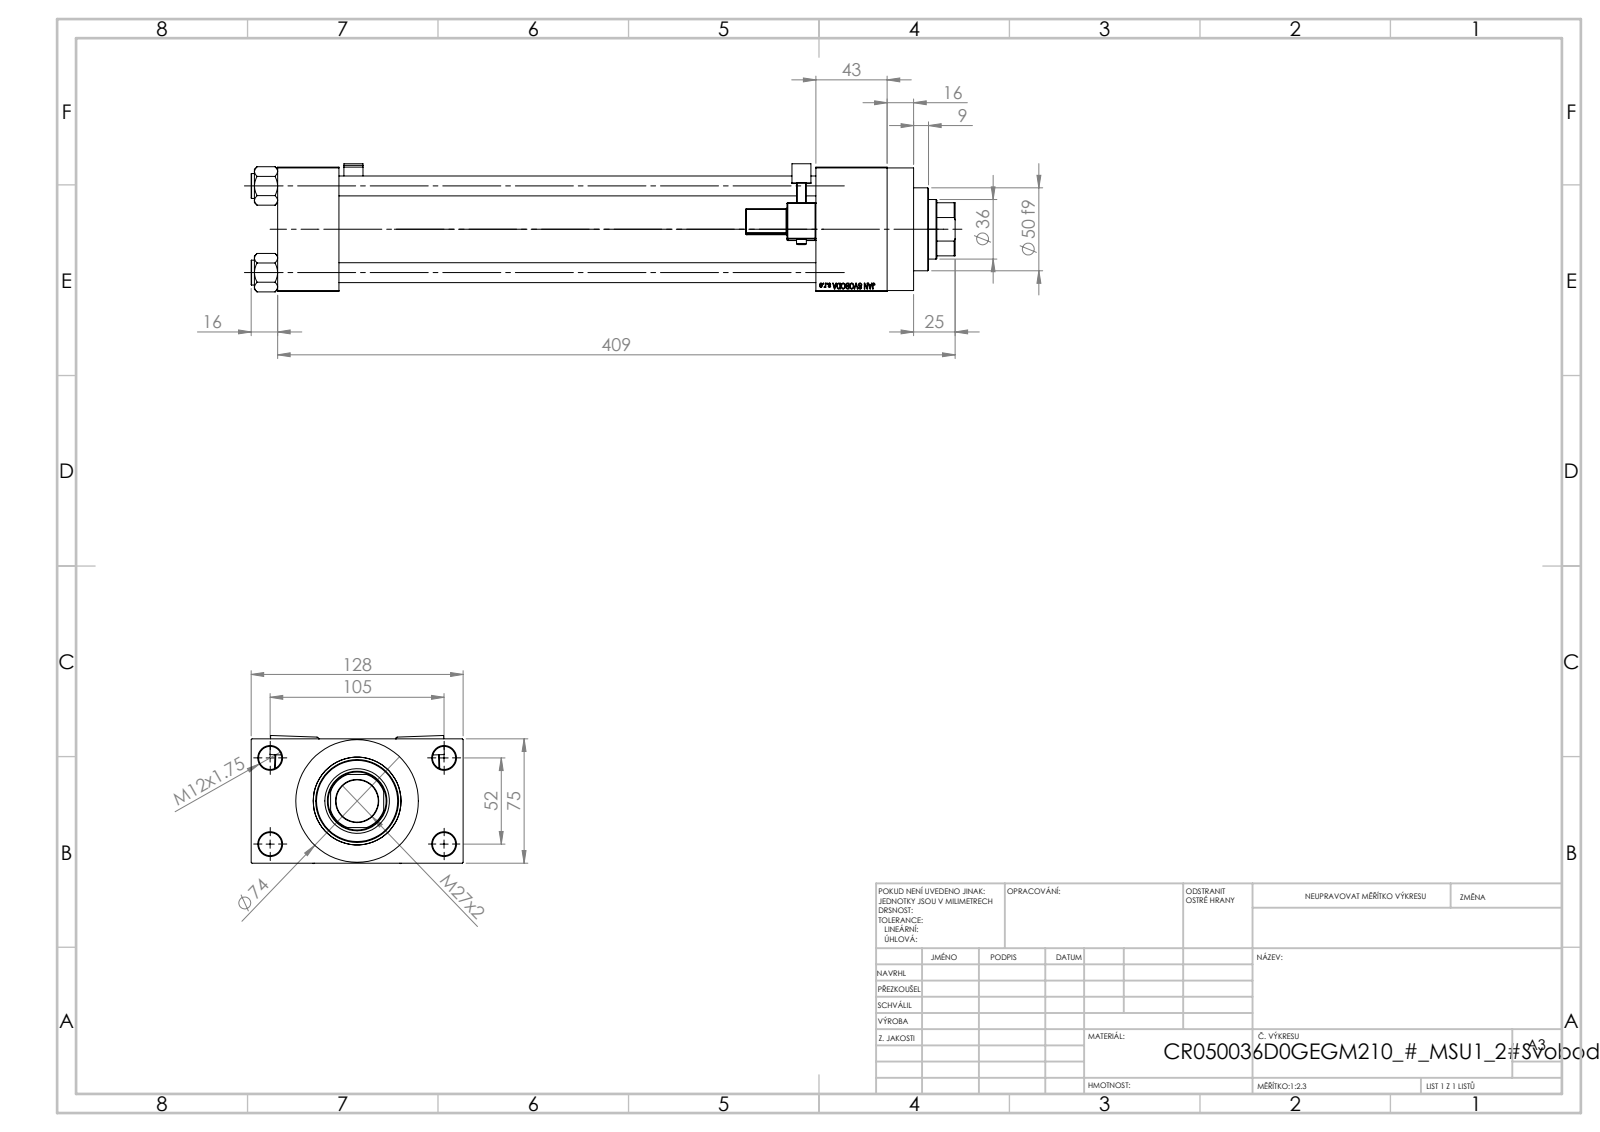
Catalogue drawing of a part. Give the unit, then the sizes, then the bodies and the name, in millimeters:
Units: millimetres
Overall size (bounding box): 425 × 128 × 77.3
Round holes (diameter × count): ⌀12 ×4, ⌀14 ×4, ⌀7 ×2, ⌀20.96 ×2, ⌀30 ×2, ⌀25.5 ×1, ⌀36 ×1, ⌀39 ×1, ⌀41 ×1, ⌀53 ×1
Round bosses / shafts (diameter × count): ⌀15 ×4, ⌀6 ×2, ⌀74 ×1, ⌀56 ×1, ⌀50 ×1
Partial cylindrical surfaces — rounded edges, fillets, slot ends (radius × count): R0.5 ×48, R1 ×2, R2.5 ×2, R4 ×2, R17.5 ×1
Main face-to-face distances: 75, 288, 101.5, 37, 325, 26.5, 43, 368, 331, 16
Hole centre spacings: 26.35, 36.98, 52.3, 58.43, 58.59, 78.65, 94.37, 52
Volume: 1 321 000 mm³ · Surface area: 323 344 mm²
Bodies: 13 solids, 1258 faces (555 planar, 149 cylindrical, 554 other)
Part name (STEP PRODUCT): V215CR_MSU; V215CR_VCP_D; V215CR_D_Body; V215_VC_A (+2 more)
STEP written by: SolidWorks 2019 (CONFIG_CONTROL_DESIGN)
